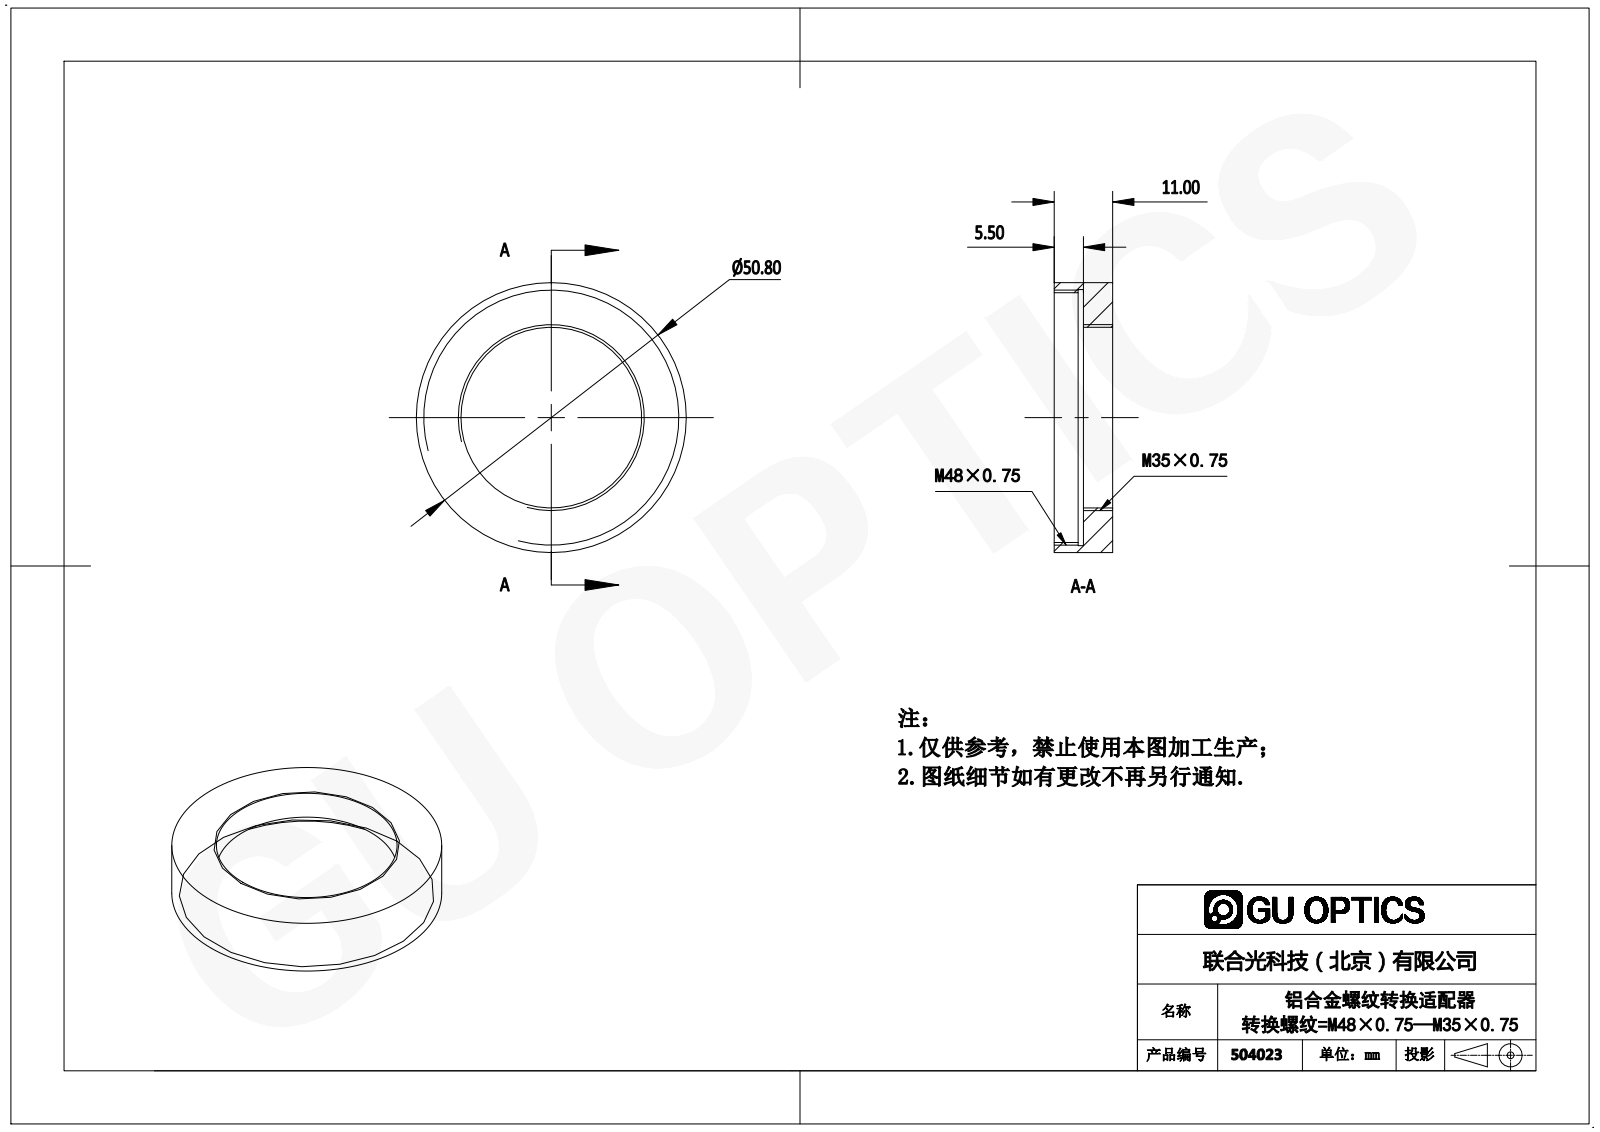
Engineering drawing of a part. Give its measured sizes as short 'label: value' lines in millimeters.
name: 504023
written by: SolidWorks 2016 (AUTOMOTIVE_DESIGN)
unit: mm
bodies: 1 solid, 12 faces (4 planar, 8 cylindrical, 0 other)
size: 50.8 × 50.8 × 11
volume: 7 670 mm³; area: 5 576 mm²
holes: 1× ⌀34, 1× ⌀47, 1× ⌀48.2
bosses: 1× ⌀50.8
face distances: 5.5, 11, 4.5, 1, 6.5
